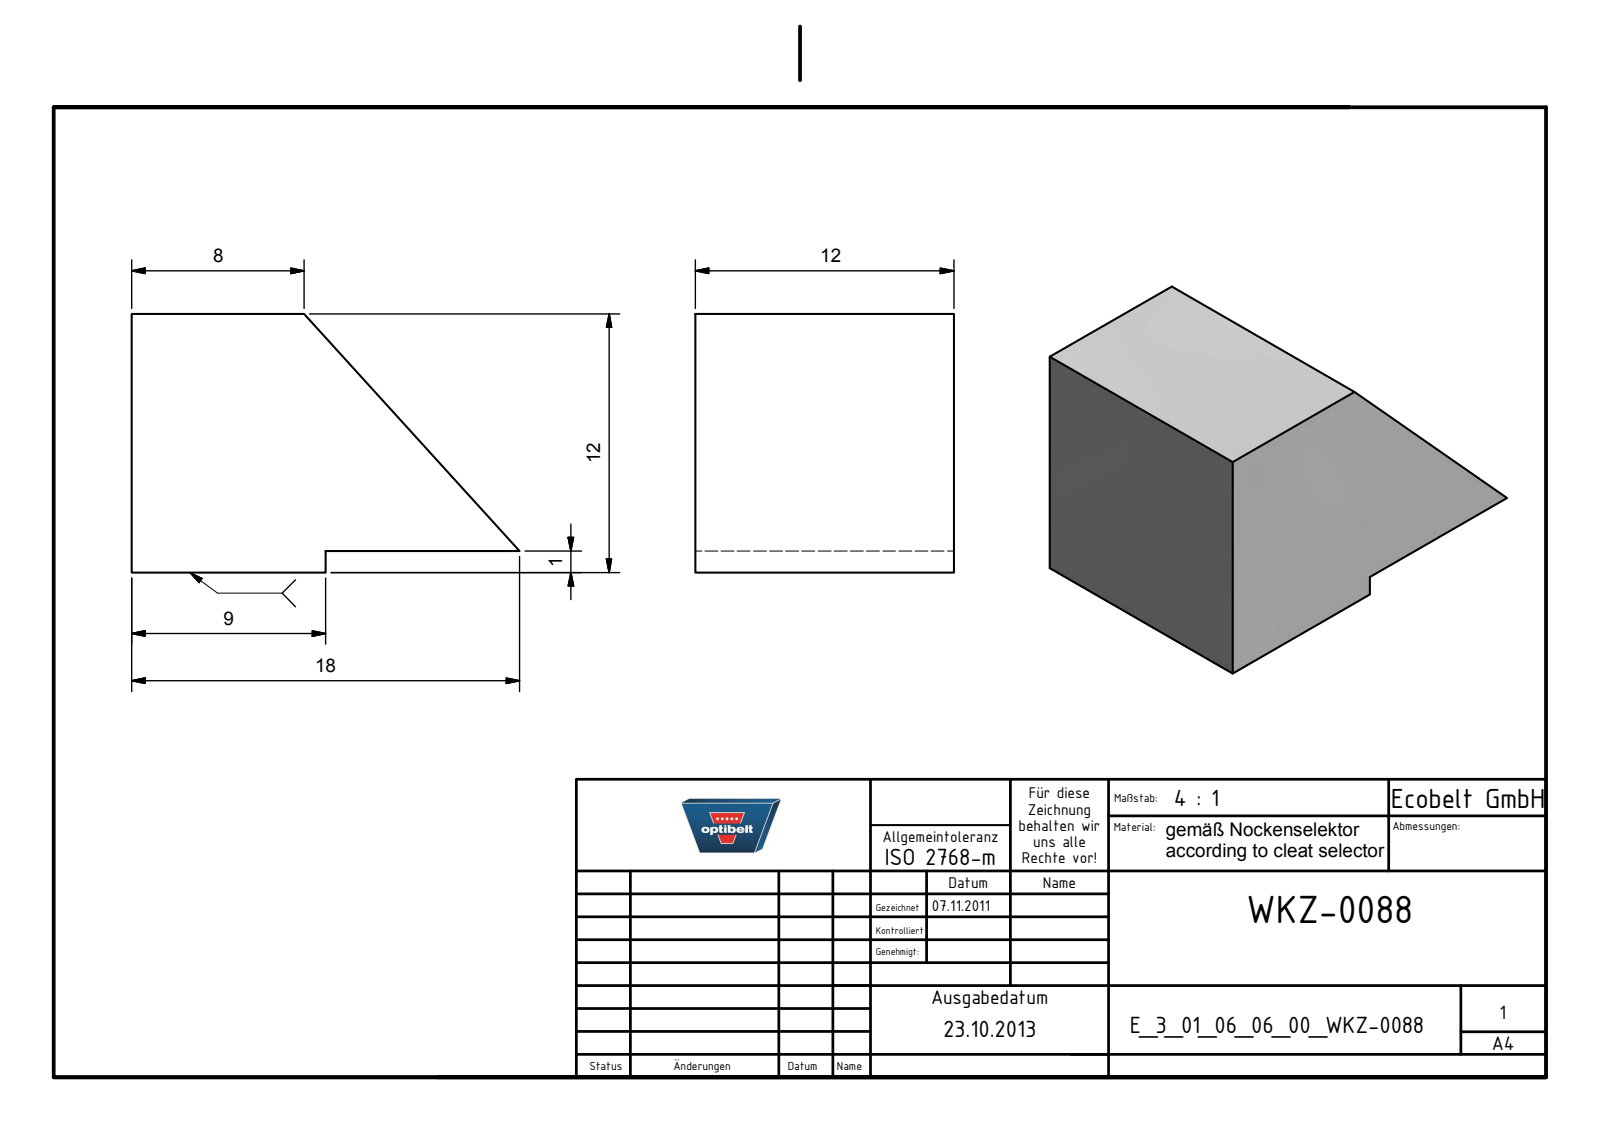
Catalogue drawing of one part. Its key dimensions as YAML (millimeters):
part_name: "E_3_01_06_06_00_WKZ-0088"
step_written_by: "Autodesk Inventor 2025 (AUTOMOTIVE_DESIGN)"
units: millimeters
bodies: {solids: 1, faces: 8, planar: 8, cylindrical: 0, other: 0}
overall_size: [18, 12, 12]
volume: 1824
surface_area: 950
face_to_face_distances: [12, 1, 11, 9]
